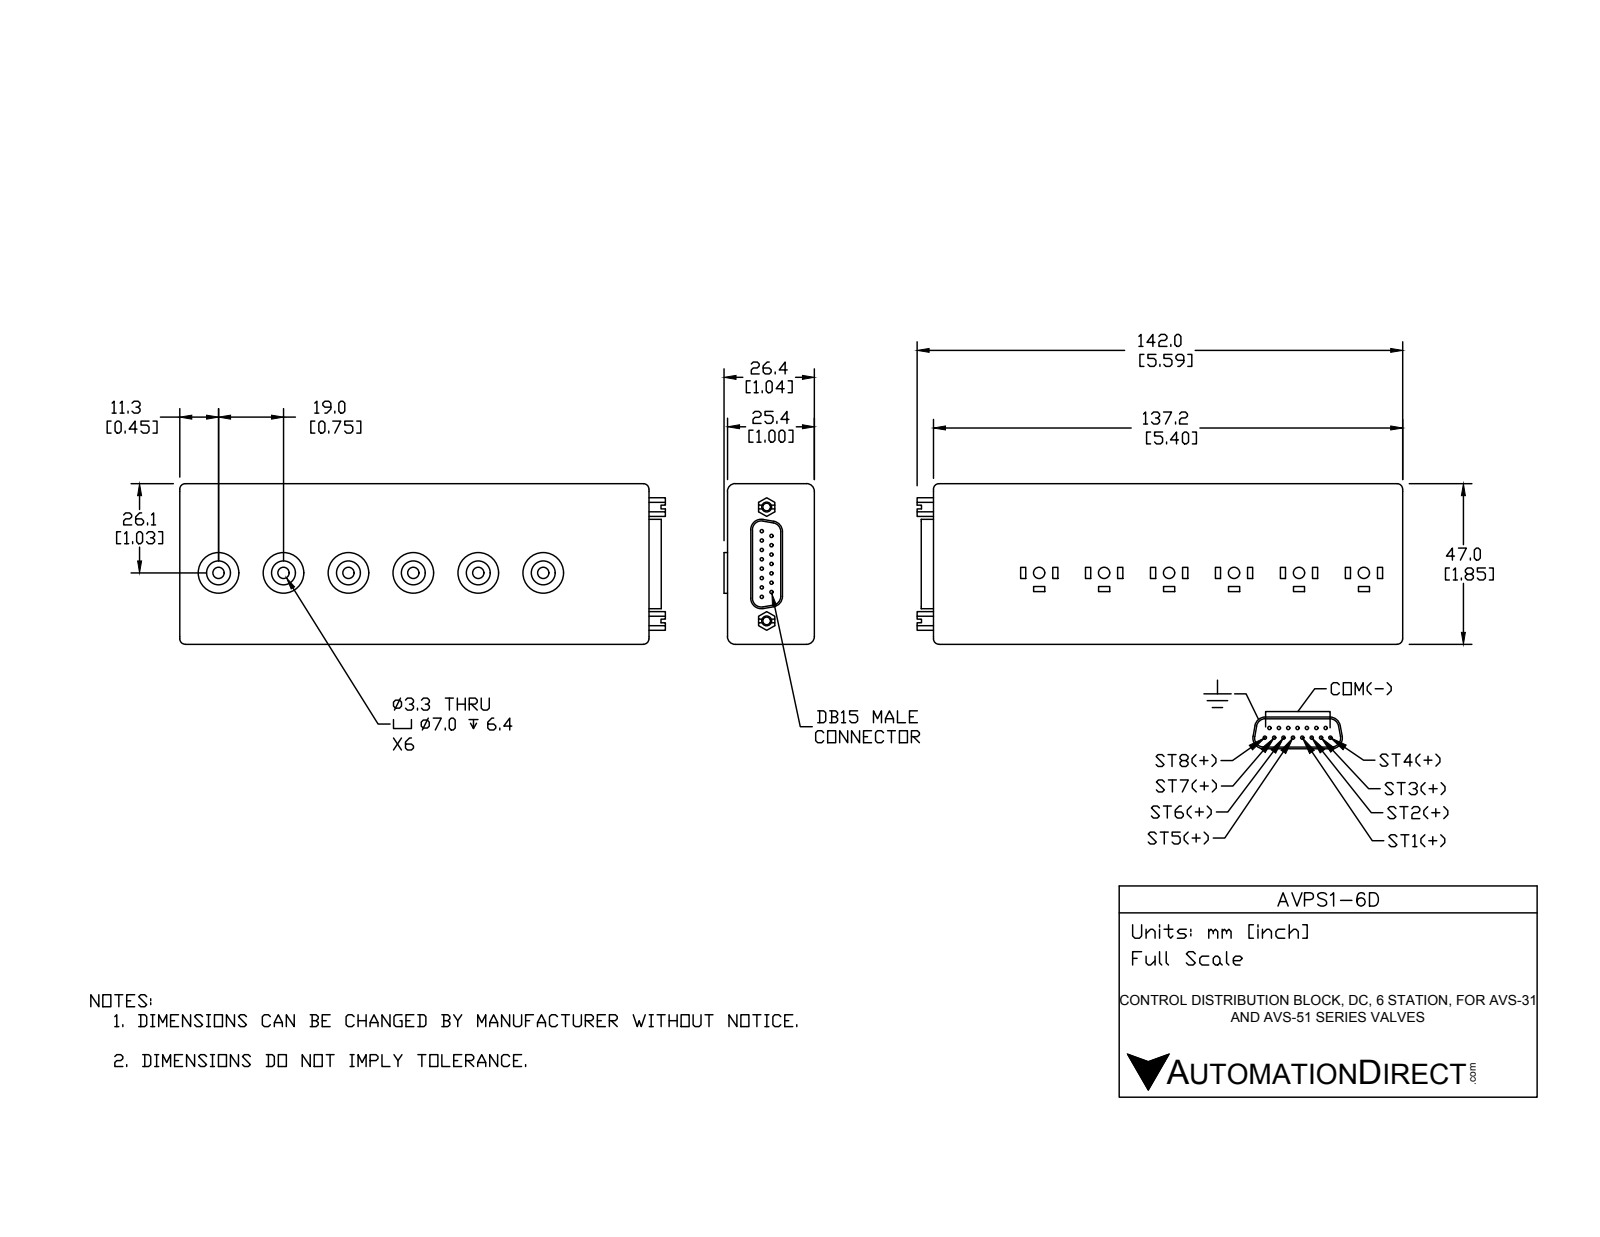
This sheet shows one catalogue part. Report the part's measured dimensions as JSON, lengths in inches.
{"part_name": "AVPS1-6D", "step_written_by": "SolidWorks 2016 (AUTOMOTIVE_DESIGN)", "units": "inches", "bodies": {"solids": 1, "faces": 265, "planar": 161, "cylindrical": 92, "other": 12}, "overall_size": [5.592, 1.85, 1.04], "volume_in3": 9.787, "surface_area_in2": 40.21, "round_holes": [[0.13, 6], [0.275, 6], [0.089, 2]], "round_bosses_or_shafts": [[0.039, 15], [0.469, 6]], "partial_cylinders_radius": [[0.062, 8], [0.09, 4], [0.102, 4], [0.122, 4]], "face_to_face_distances": [1, 1.85, 5.403, 0.04, 1.04, 0.25, 0.79, 0.059, 0.748, 0.123], "hole_center_spacings": [0.748, 1.496, 2.244, 2.992, 1.311, 3.74]}
